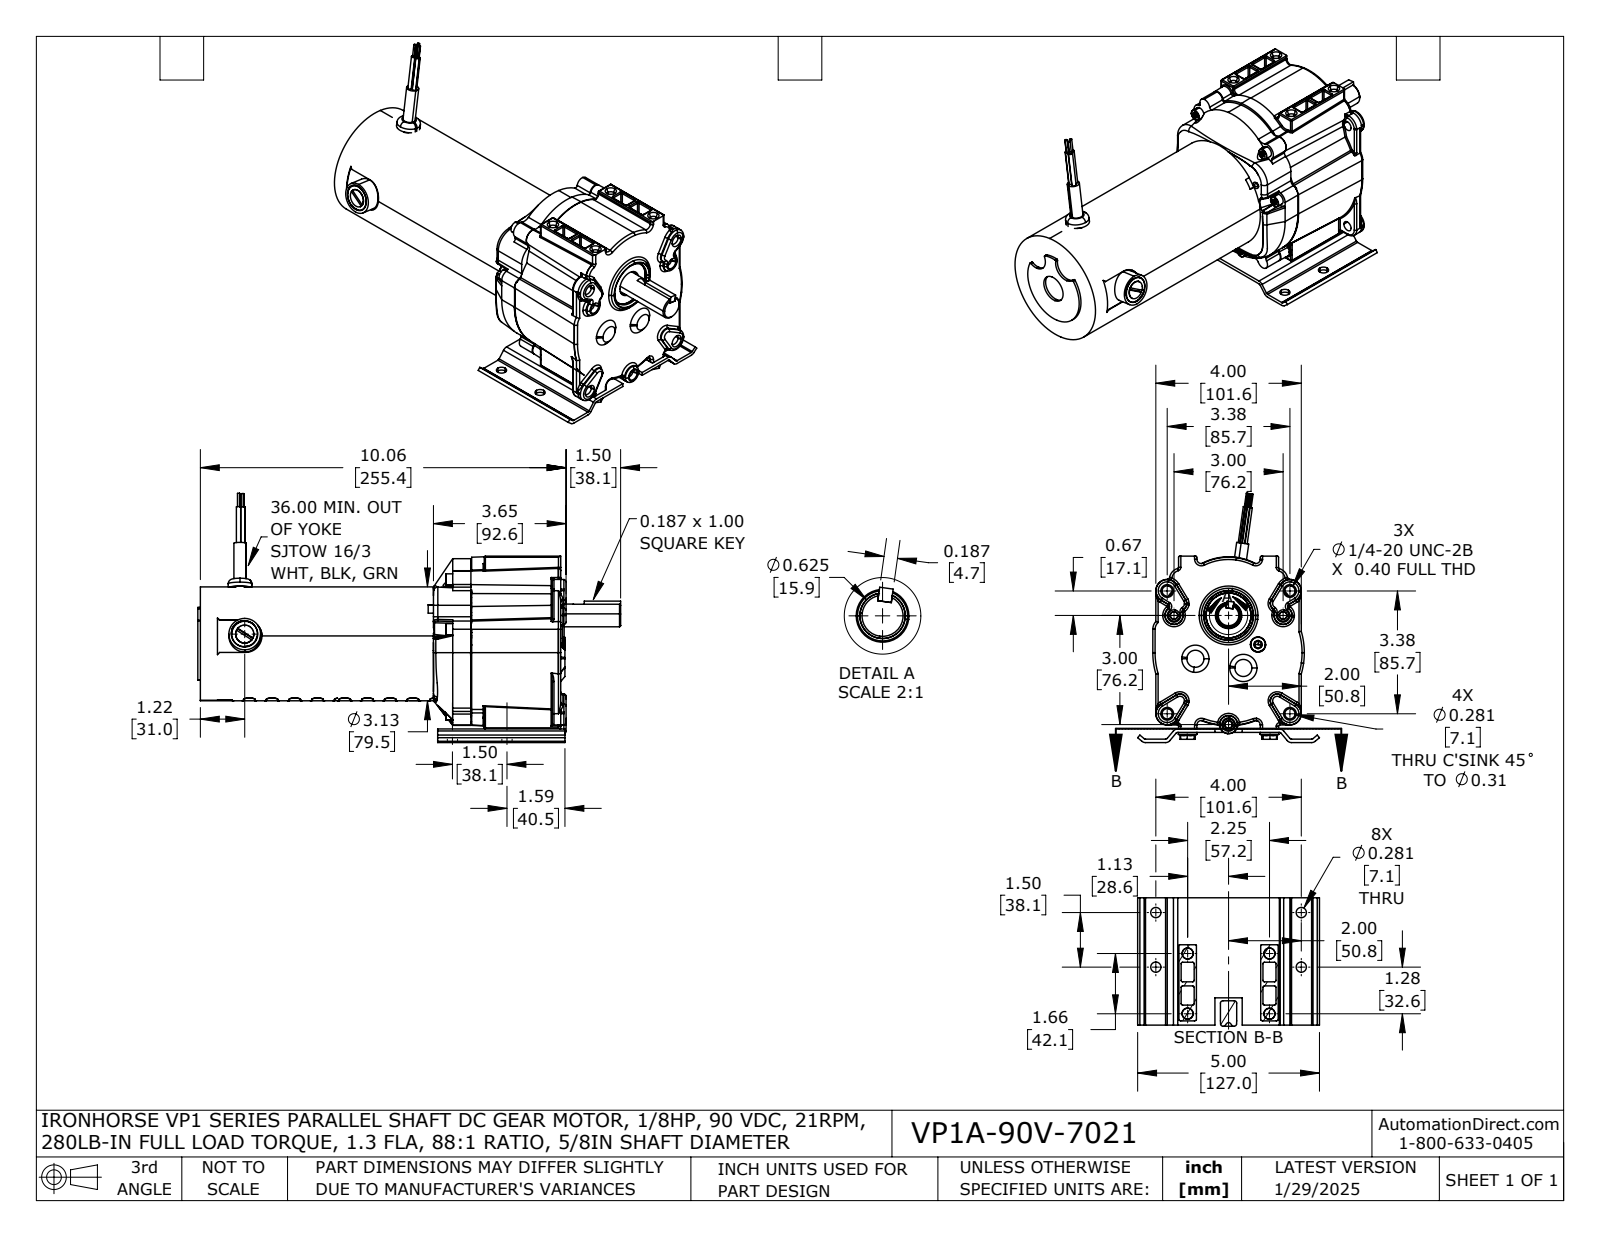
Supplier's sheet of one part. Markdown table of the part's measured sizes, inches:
| quantity | value |
| --- | --- |
| part name | VP1A-90V-7021 |
| STEP written by | SolidWorks 2024 (AUTOMOTIVE_DESIGN) |
| units | inches |
| bodies | 10 solids, 2472 faces (654 planar, 701 cylindrical, 1117 other) |
| overall size | 11.627 × 6.854 × 5 |
| volume | 98.93 in³ |
| surface area | 345.4 in² |
| round holes (diameter × count) | 0.281 × 12, 0.218 × 5, 0.159 × 3, 0.207 × 3, 0.135 × 2, 0.166 × 2, 0.204 × 2, 0.397 × 2, 0.688 × 2, 0.875 × 2, 0.75 × 1, 0.813 × 1 |
| round bosses / shafts (diameter × count) | 0.307 × 5, 0.19 × 5, 0.51 × 4, 0.3 × 4, 0.12 × 3, 0.06 × 3, 0.873 × 2, 0.733 × 2 |
| partial cylindrical surfaces (radius × count) | 0.03 × 52, 0.031 × 38, 0.062 × 23, 0.12 × 18, 0.156 × 18, 0.19 × 10, 0.151 × 9, 0.161 × 9 |
| main face-to-face distances | 0.095, 2.449, 3.5, 1.051, 9.44, 6.991, 5.94, 0.47, 6.97, 9.91 |
| hole center spacings | 1.5, 3.375, 1.691, 0.492, 0.698, 1.224, 1.426, 1.552 |
